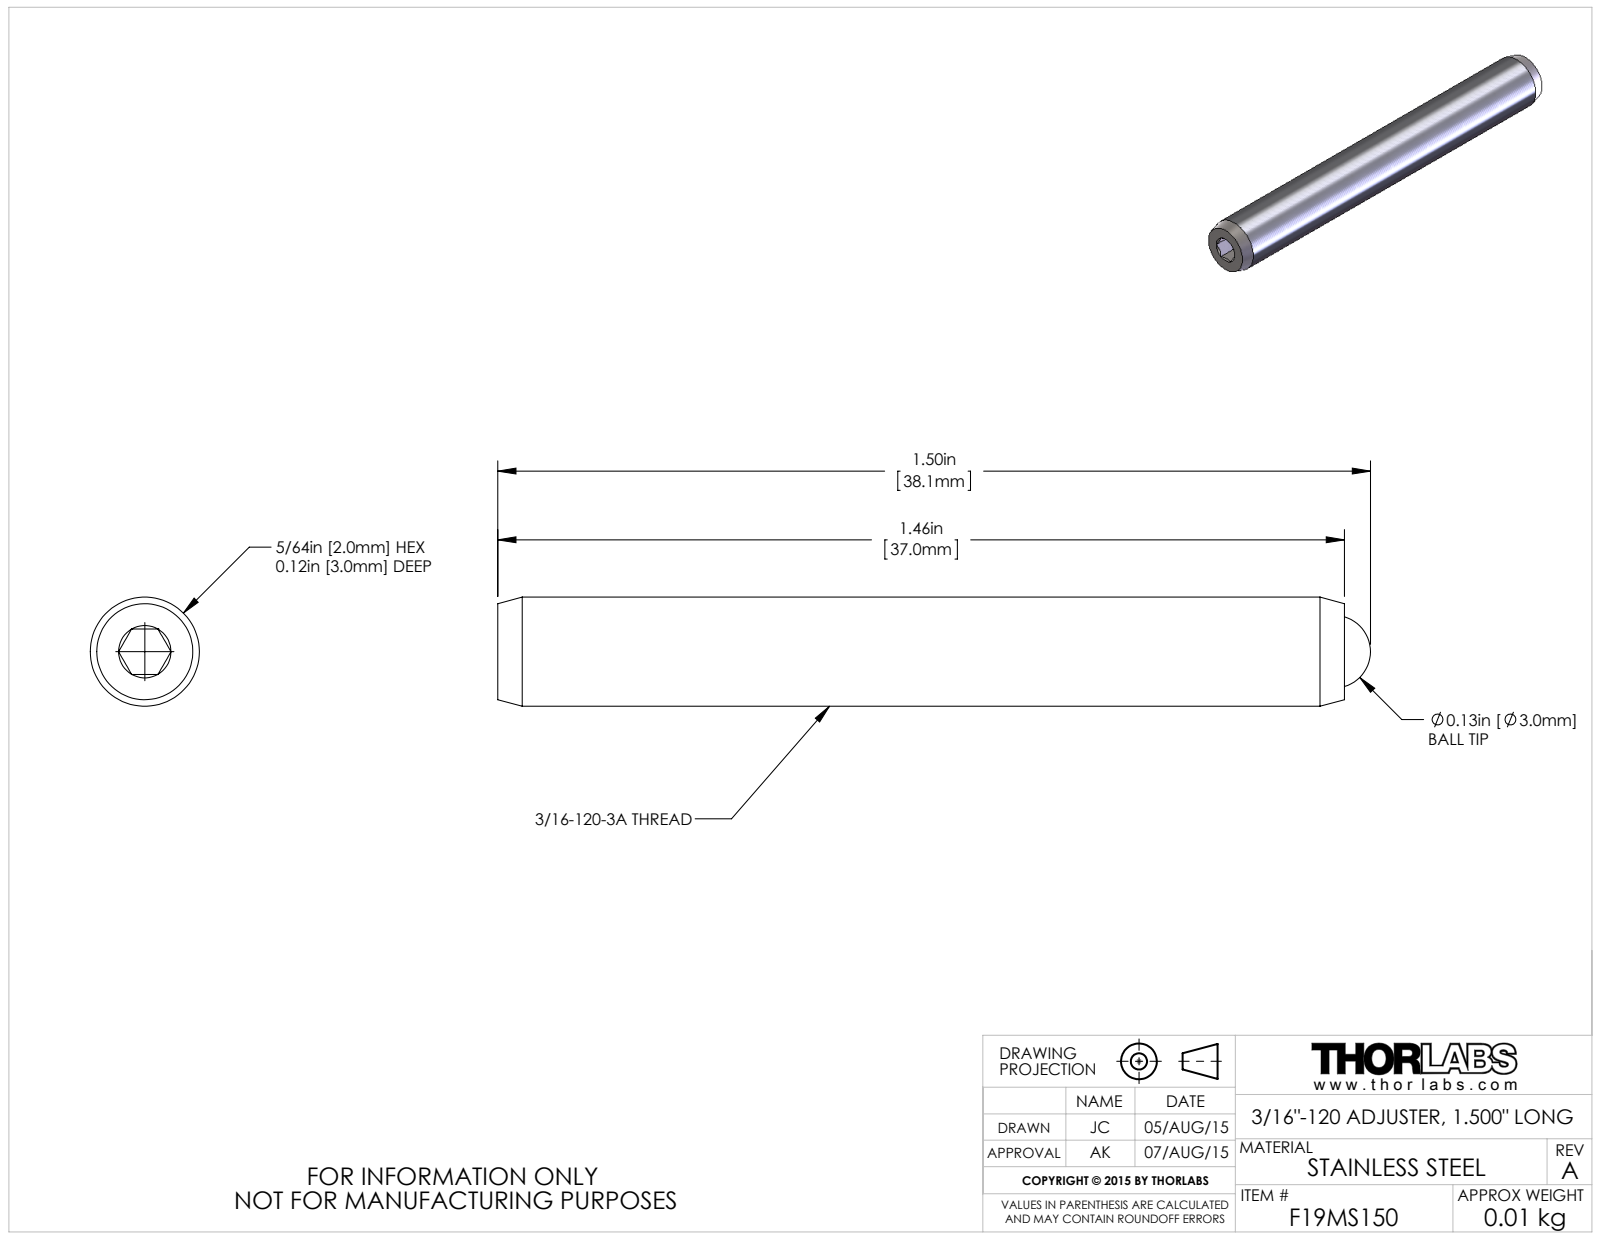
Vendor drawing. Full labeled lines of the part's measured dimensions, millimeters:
Part name (STEP PRODUCT): TTN045707-E0W
STEP written by: SolidWorks 2014 (AUTOMOTIVE_DESIGN)
Units: millimetres
Bodies: 2 solids, 29 faces (9 planar, 4 cylindrical, 16 other)
Overall size (bounding box): 38.1 × 4.8 × 4.7
Volume: 640 mm³ · Surface area: 646 mm²
Round holes (diameter × count): ⌀3.2 ×1
Round bosses / shafts (diameter × count): ⌀4.7 ×1
Main face-to-face distances: 2, 37, 3, 33.9, 2
